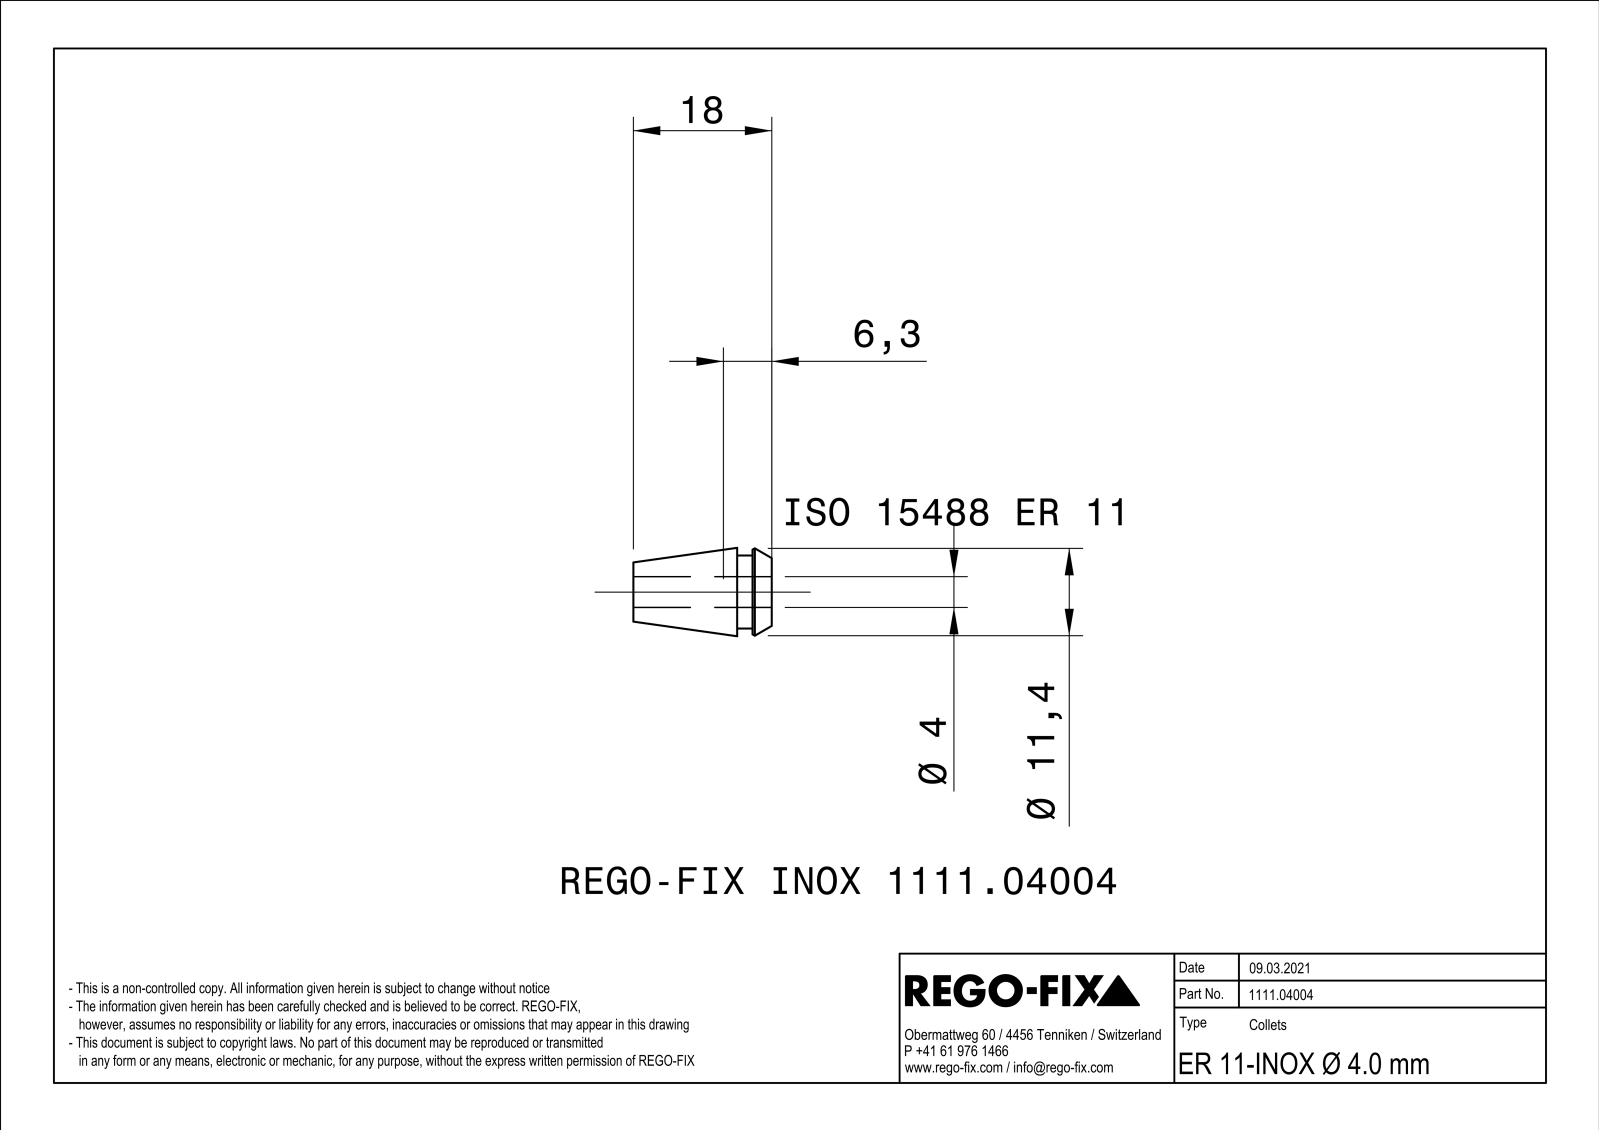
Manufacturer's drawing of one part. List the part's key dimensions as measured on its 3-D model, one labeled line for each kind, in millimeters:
Part name (STEP PRODUCT): NOCUT
STEP written by: SIEMENS PLM Software Solid Edge ST10 (AUTOMOTIVE_DESIGN)
Units: millimetres
Bodies: 1 solid, 157 faces (66 planar, 37 cylindrical, 54 other)
Overall size (bounding box): 18 × 11.5 × 11.49
Volume: 892 mm³ · Surface area: 1 757 mm²
Round holes (diameter × count): ⌀4 ×1
Round bosses / shafts (diameter × count): ⌀11.5 ×1, ⌀9.5 ×1
Partial cylindrical surfaces — rounded edges, fillets, slot ends (radius × count): R25 ×12
Main face-to-face distances: 0.45, 0.46, 0.44, 2.5, 4.5, 2, 18, 15.5, 13.5, 4
